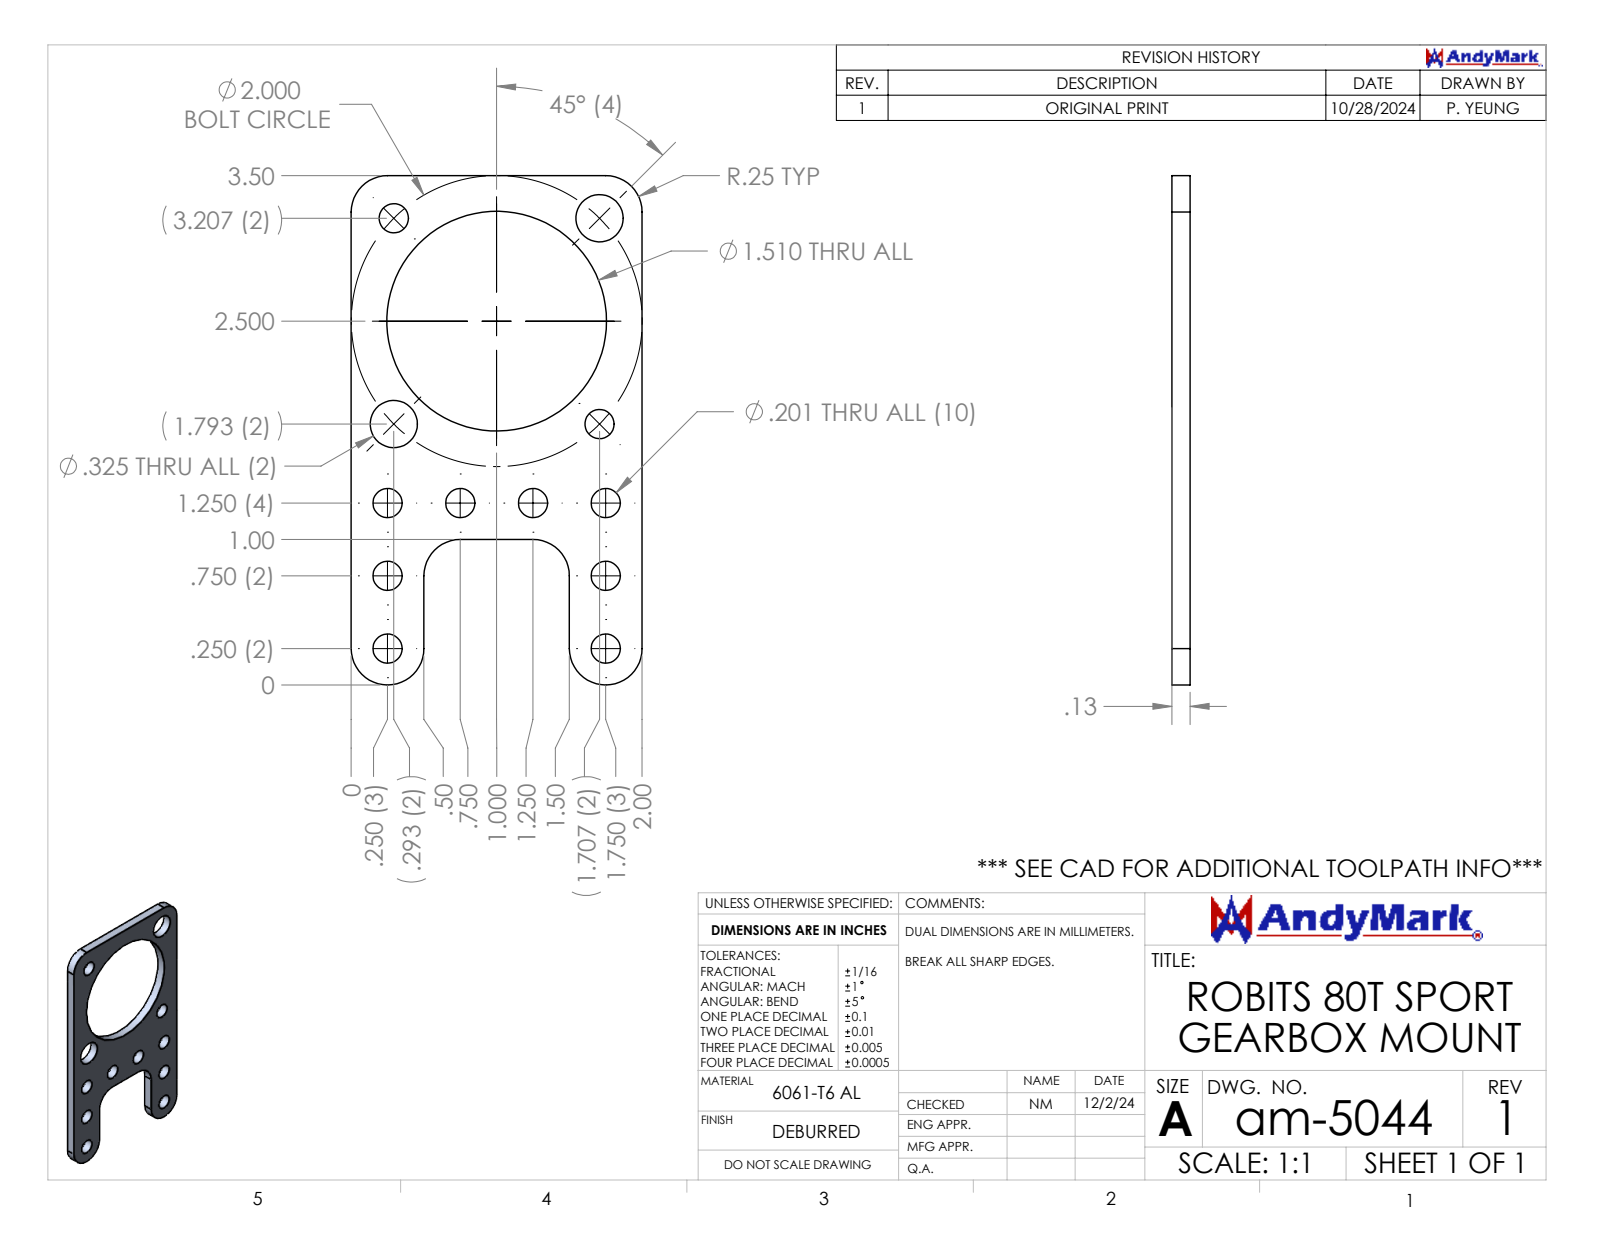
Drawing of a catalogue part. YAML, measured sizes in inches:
part_name: "am-5044 Robits 80T Sport Gearbox Mount"
step_written_by: "SolidWorks 2024 (AUTOMOTIVE_DESIGN)"
units: inches
bodies: {solids: 1, faces: 42, planar: 8, cylindrical: 34, other: 0}
overall_size: [3.5, 2, 0.125]
volume: 0.459
surface_area: 10.5
round_holes:
  - {diameter: 0.201, count: 10}
  - {diameter: 0.325, count: 1}
  - {diameter: 0.325, count: 1}
  - {diameter: 1.51, count: 1}
partial_cylinders:
  - {radius: 0.25, count: 6}
face_to_face_distances: [0.125, 2, 0.5, 1.5, 2.5, 1]
hole_center_spacings: [1, 0.5, 1.414, 1.118, 1.581, 1.5, 0.544, 0.707]
